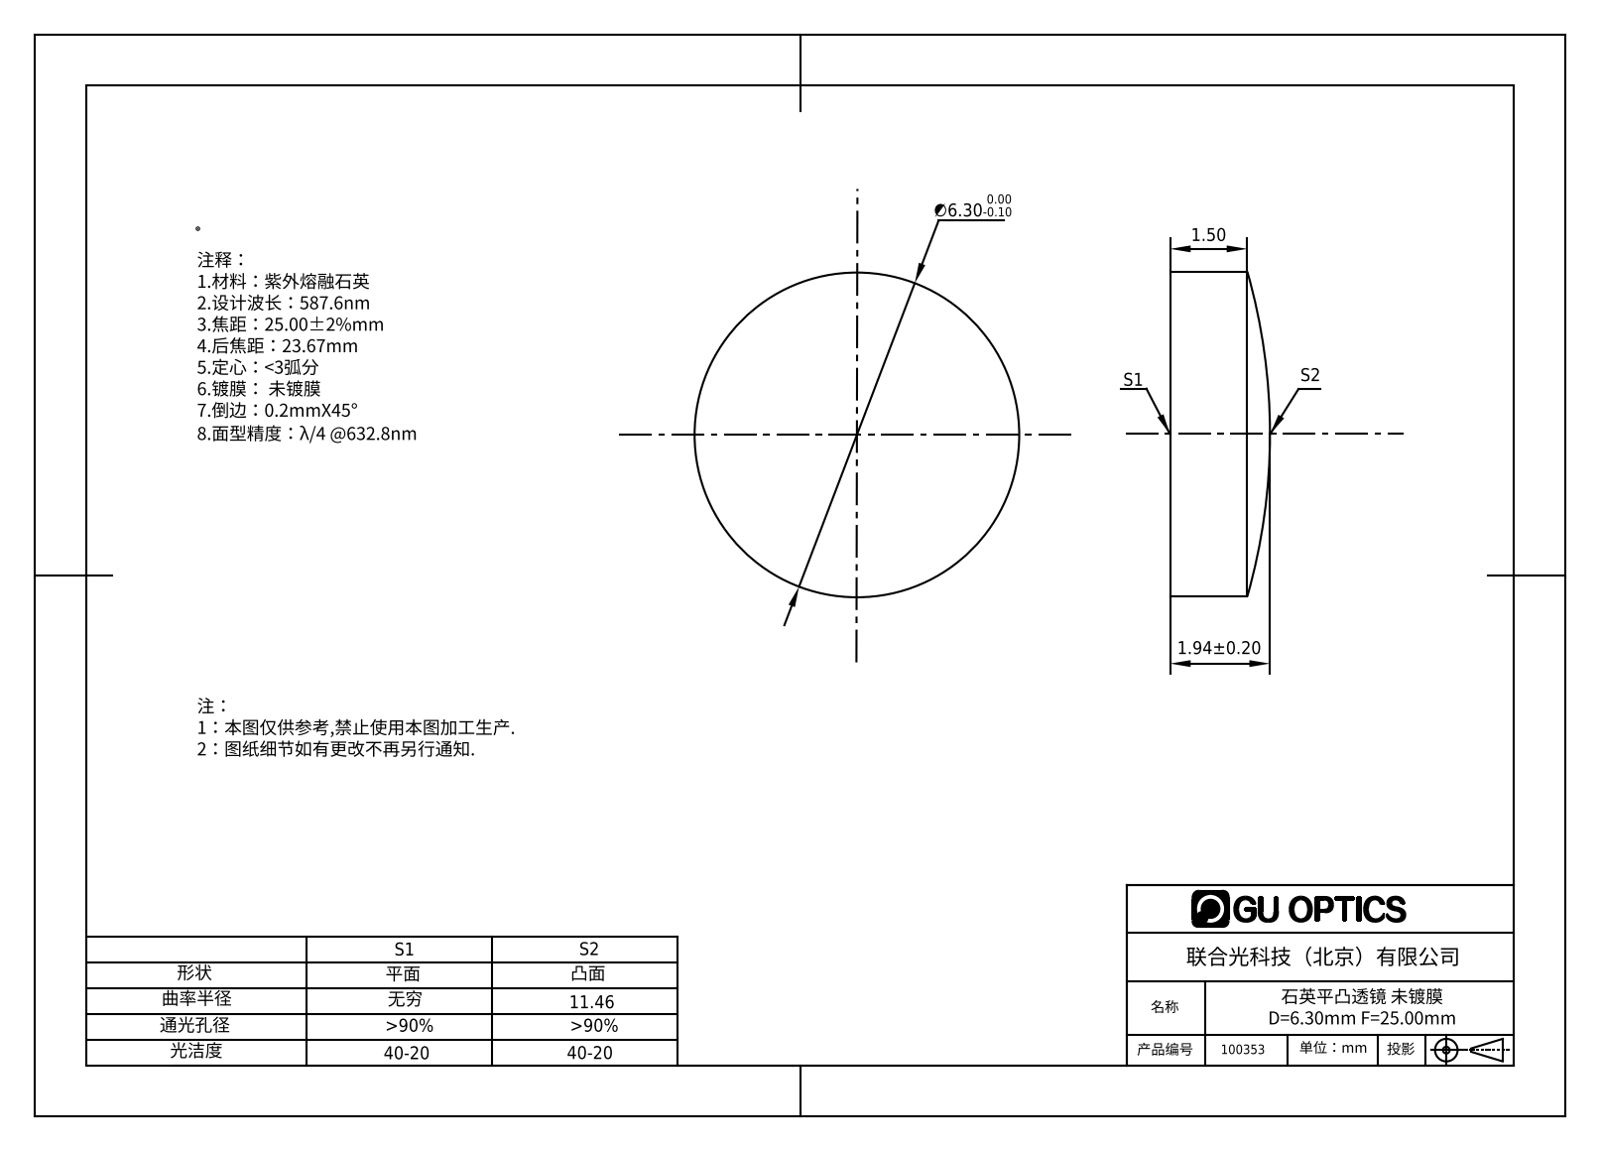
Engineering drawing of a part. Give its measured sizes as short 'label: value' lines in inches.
name: 100353
written by: SolidWorks 2016 (AUTOMOTIVE_DESIGN)
unit: in
bodies: 1 solid, 5 faces (1 planar, 2 cylindrical, 2 other)
size: 0.248 × 0.248 × 0.076
volume: 0.003 in³; area: 0.14 in²
bosses: 1× ⌀0.248
